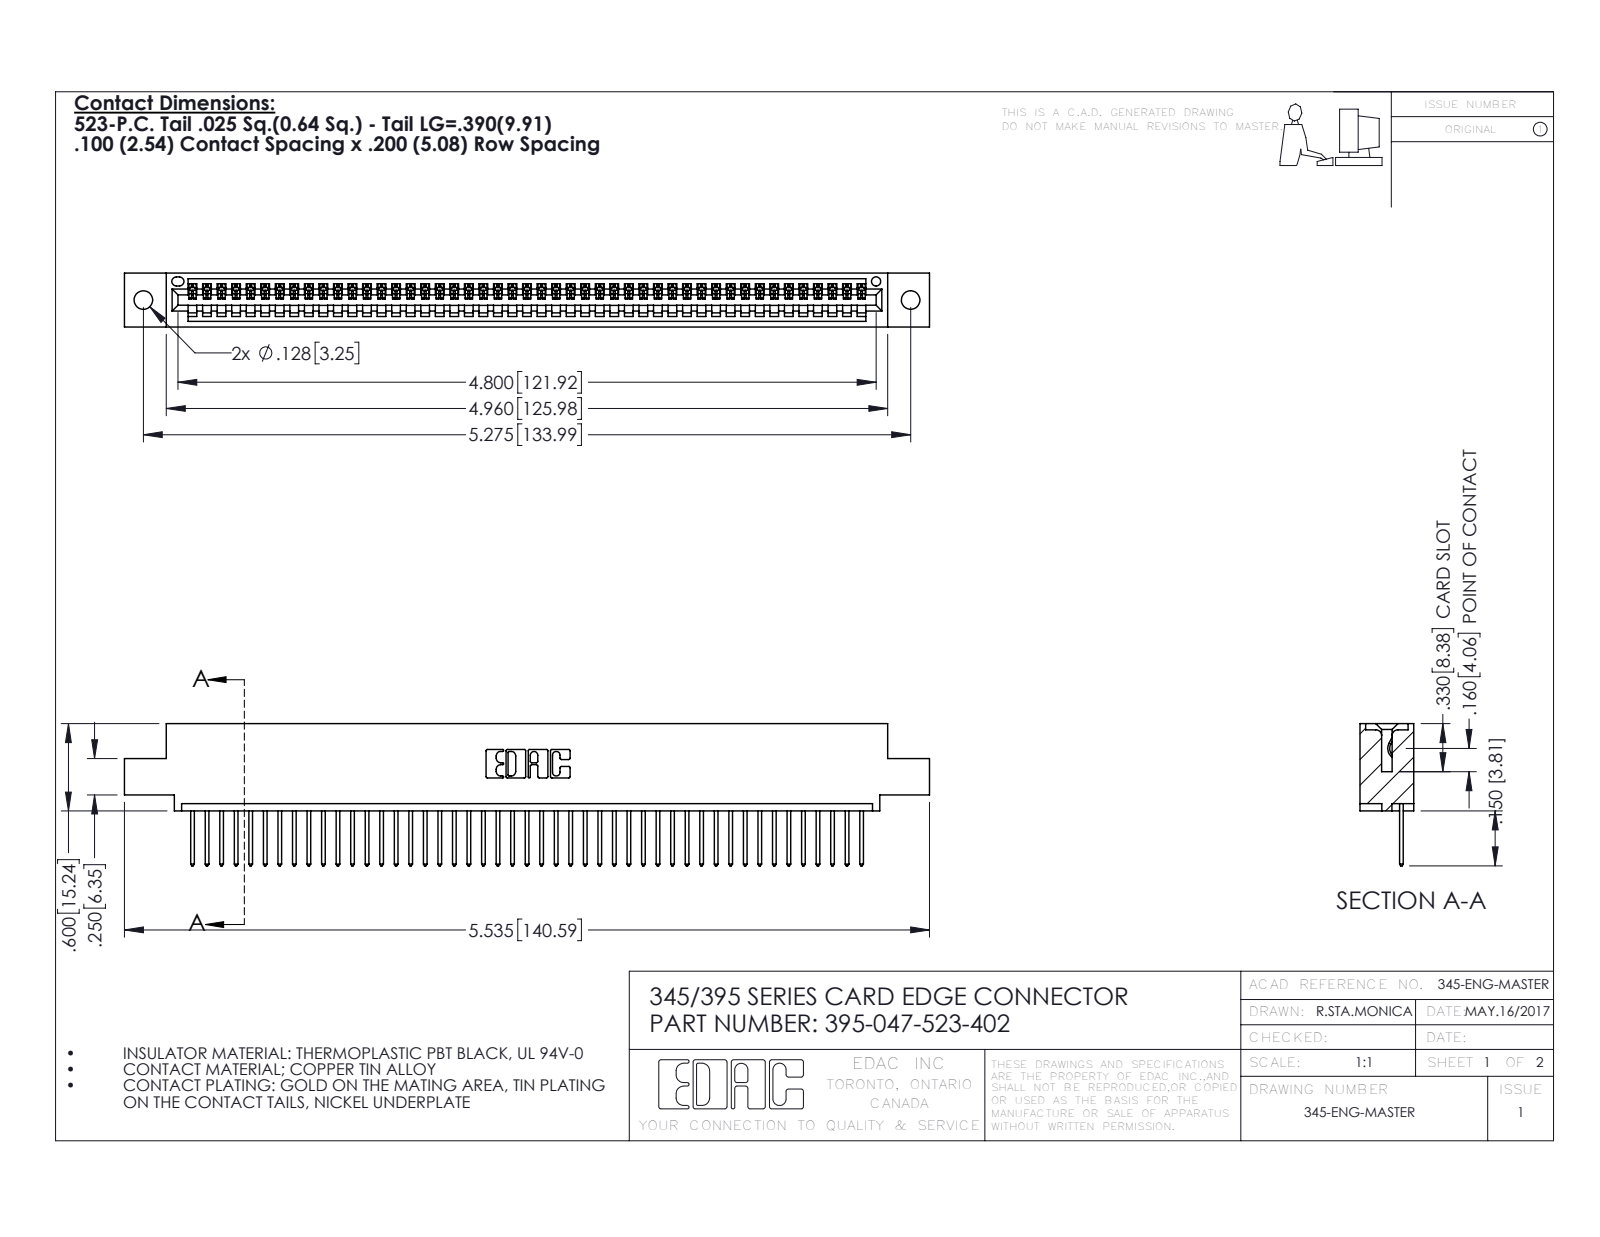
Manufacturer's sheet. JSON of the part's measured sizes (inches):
{"part_name": "395-047-523-402; 345 Part_0.110 Offset - 0.128 Dia; 345-292-001_345-293-123", "step_written_by": "SolidWorks 2016 (CONFIG_CONTROL_DESIGN)", "units": "inches", "bodies": {"solids": 48, "faces": 2856, "planar": 1964, "cylindrical": 892, "other": 0}, "overall_size": [5.535, 0.977, 0.37], "volume_in3": 0.81, "surface_area_in2": 27.22, "round_holes": [[0.128, 2], [0.064, 1]], "partial_cylinders_radius": [[0.006, 94], [0.01, 94], [0.01, 22], [0.007, 6], [0.031, 6], [0.026, 3], [0.031, 2], [0.04, 2]], "face_to_face_distances": [0.298, 0.072, 0.37, 0.2, 0.098, 0.272, 0.025, 0.225, 0.149, 0.072], "hole_center_spacings": [0.27, 5.039, 5.275]}
